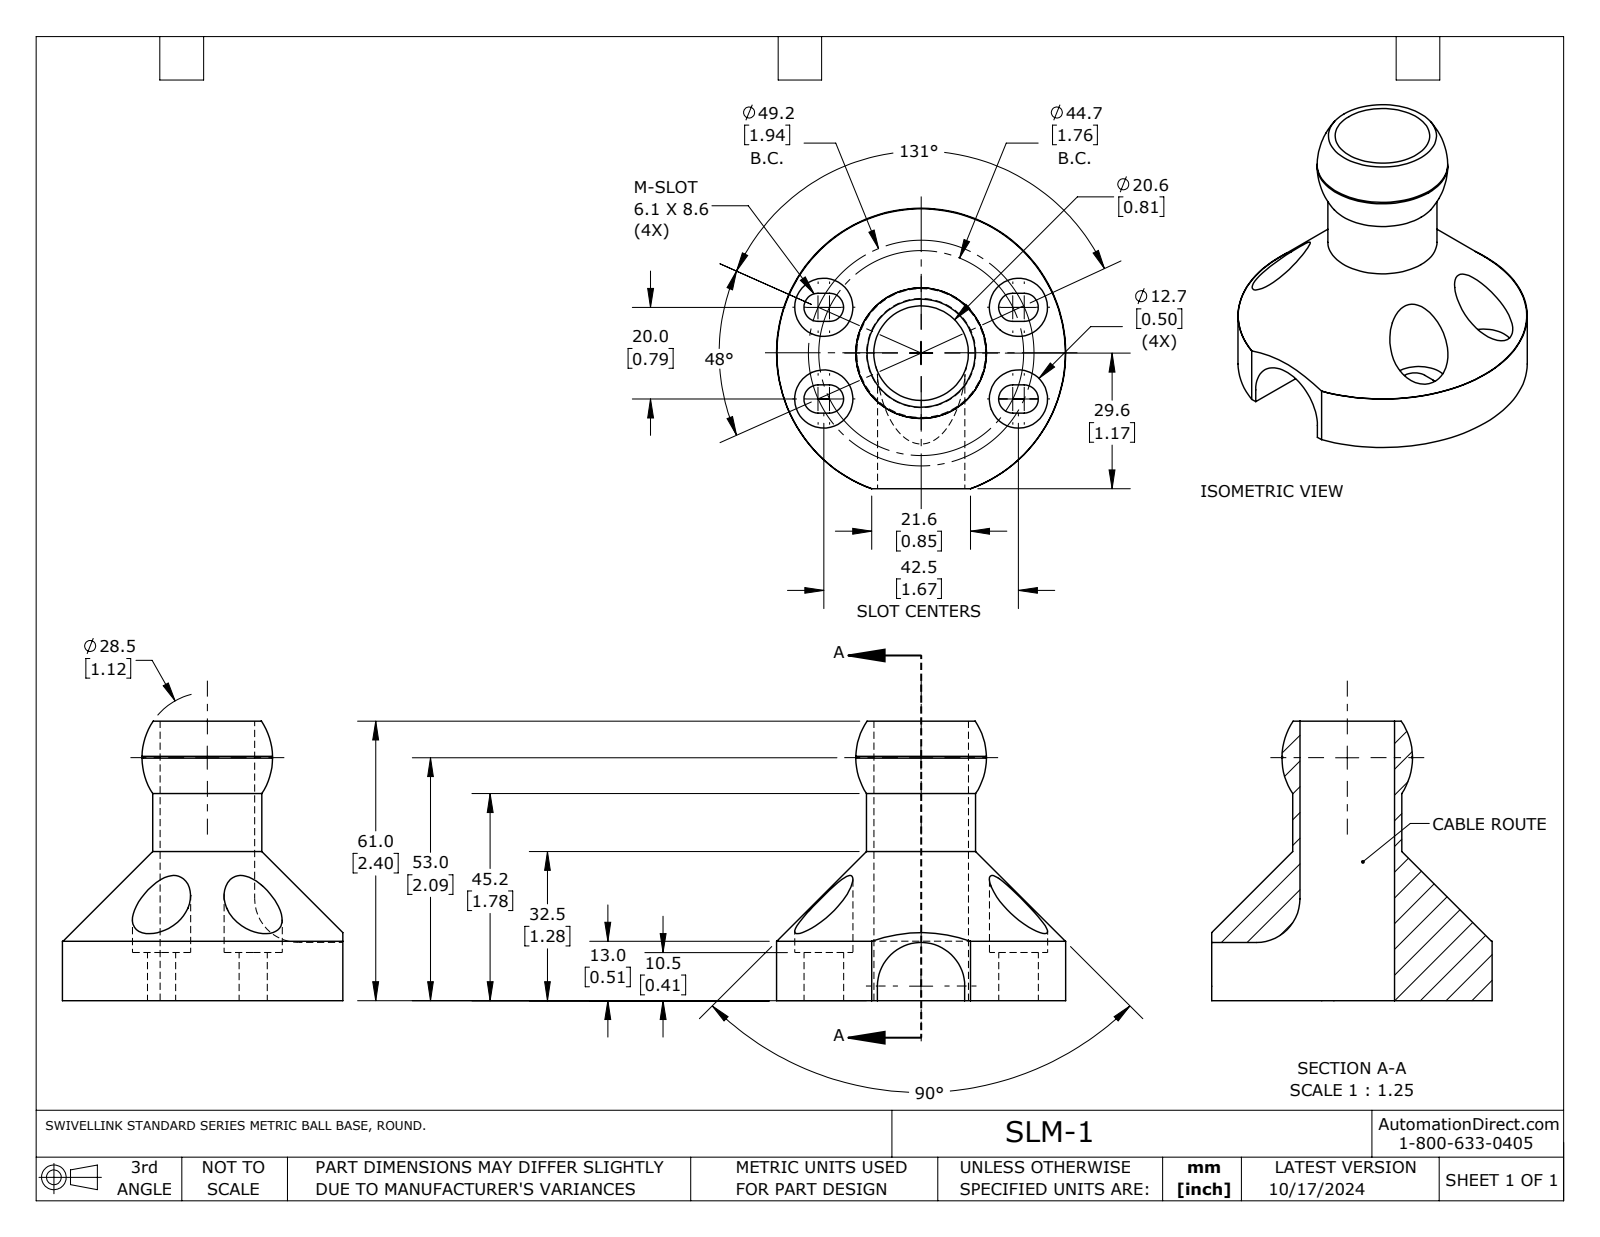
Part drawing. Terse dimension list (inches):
name: SLM-1
written by: SolidWorks 2021 (AUTOMOTIVE_DESIGN)
unit: in
bodies: 1 solid, 41 faces (18 planar, 18 cylindrical, 5 other)
size: 2.485 × 2.41 × 2.402
volume: 3.284 in³; area: 27.19 in²
holes: 4× ⌀0.5, 1× ⌀0.813
bosses: 1× ⌀2.485, 1× ⌀0.937
rounds: 8× R0.121, 3× R0.375
face distances: 0.413, 0.787, 0.242, 2.402, 1.989, 0.75, 0.65, 1.438, 0.546, 0.892
hole spacings: 0.925, 0.787, 1.673, 1.849
